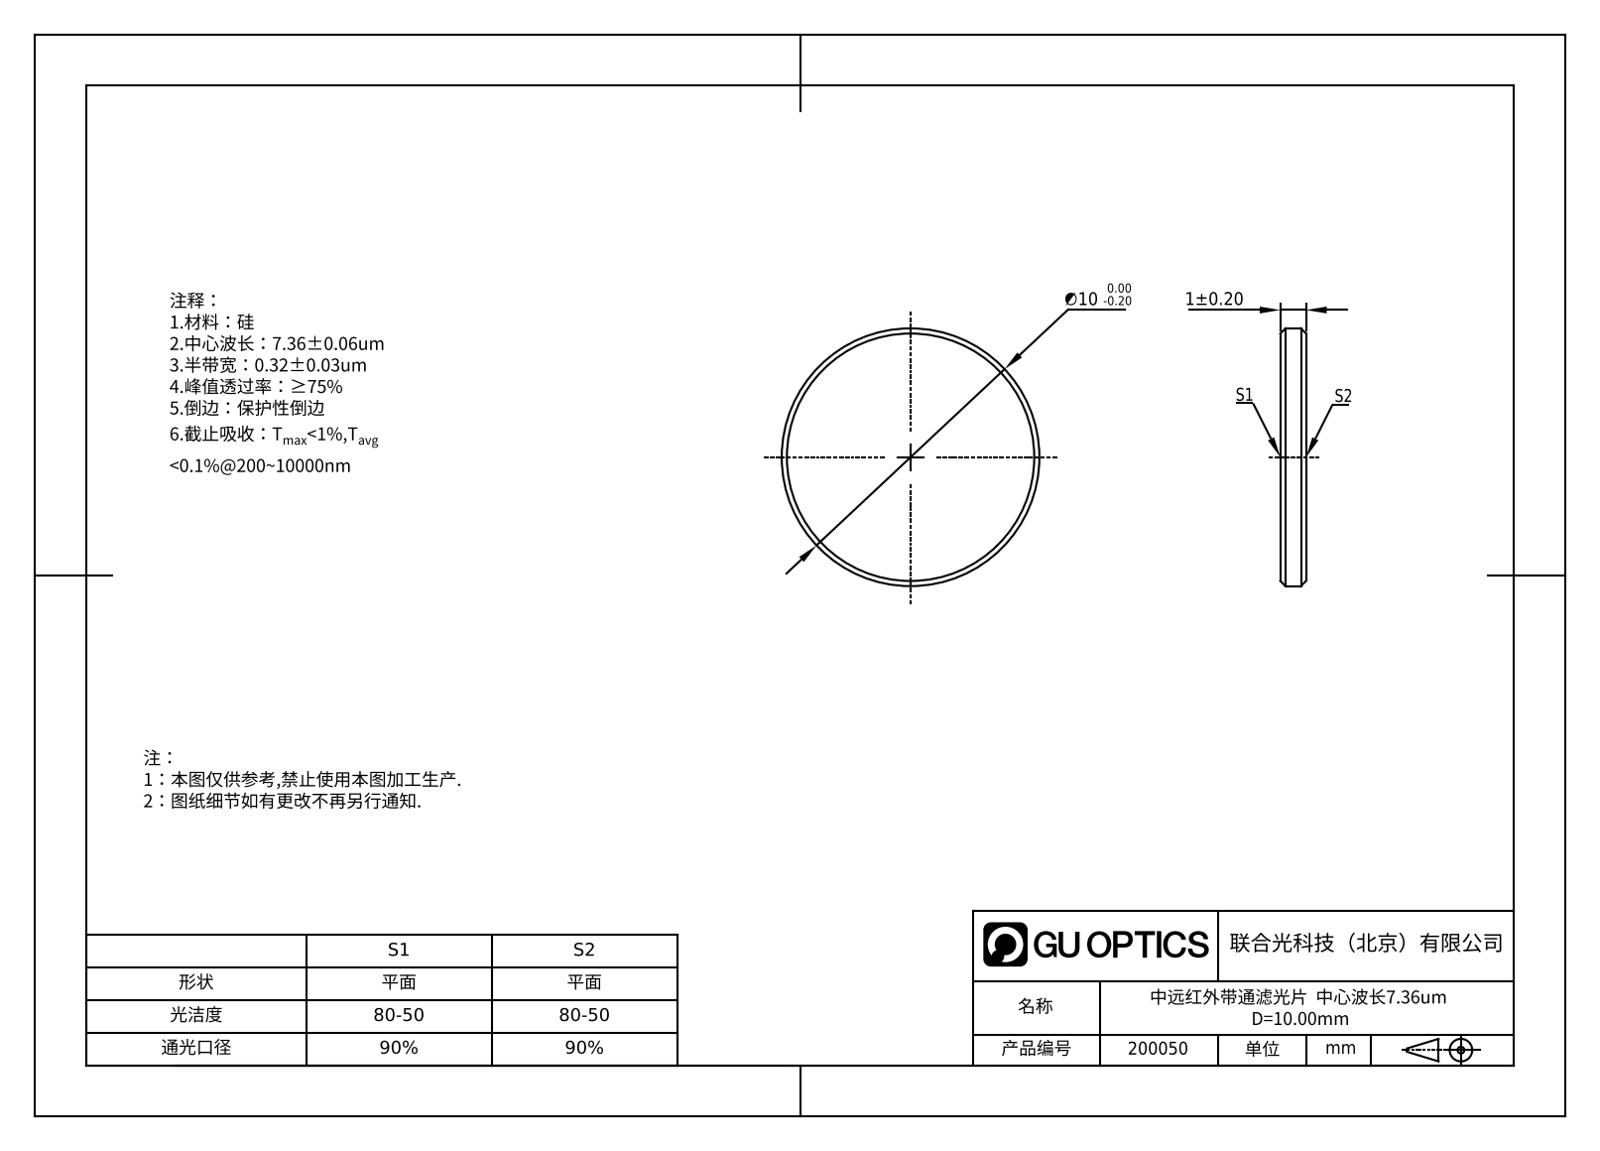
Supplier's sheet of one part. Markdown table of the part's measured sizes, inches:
| quantity | value |
| --- | --- |
| part name | GNIF-320-7360-D10 |
| STEP written by | SolidWorks 2022 (AUTOMOTIVE_DESIGN) |
| units | inches |
| bodies | 1 solid, 8 faces (2 planar, 2 cylindrical, 4 other) |
| overall size | 0.394 × 0.394 × 0.039 |
| volume | 0.005 in³ |
| surface area | 0.281 in² |
| round bosses / shafts (diameter × count) | 0.394 × 1 |
| main face-to-face distances | 0.039 |
